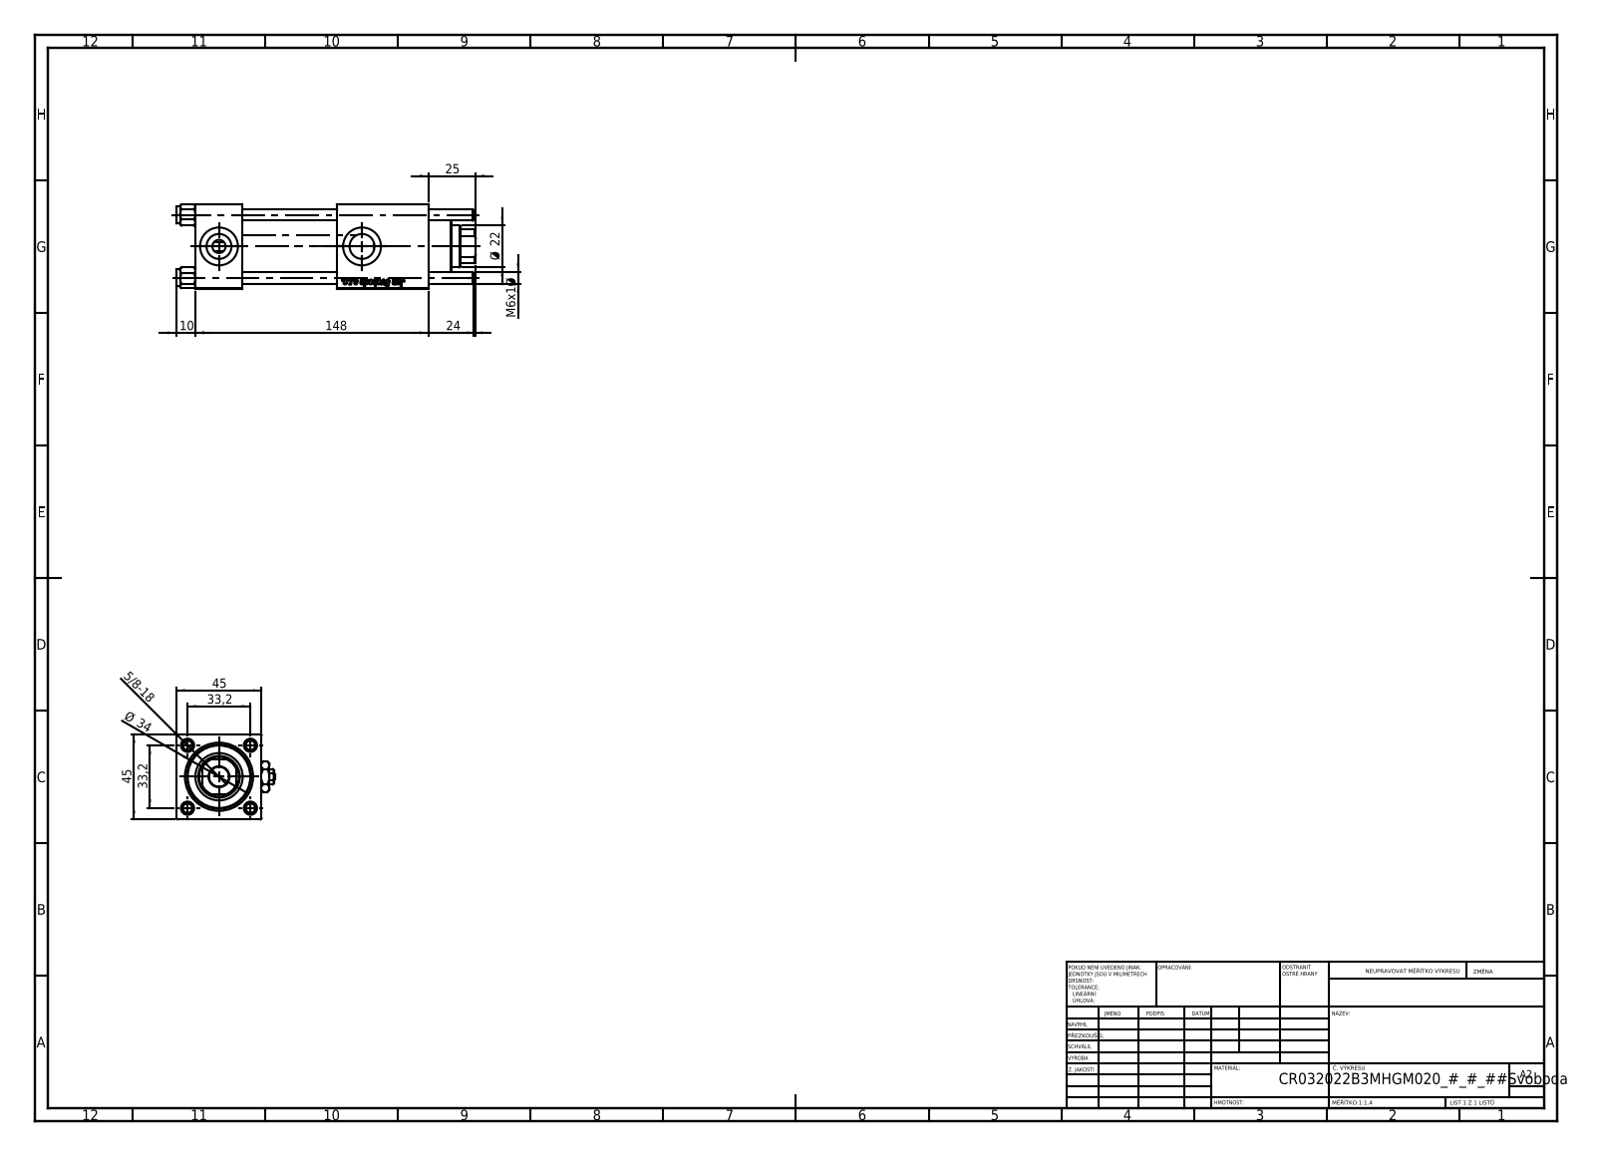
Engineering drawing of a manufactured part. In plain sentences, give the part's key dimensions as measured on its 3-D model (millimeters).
The part is named "Zatka_pro_OIL_PORT; V215_VC_A; V215CR_B_TYCINKA; NUT_M5_B (+2 more)". Its 3-D file was written by "SolidWorks 2019 (CONFIG_CONTROL_DESIGN)". It is 13 solids with 1256 faces: 478 planar, 88 cylindrical and 690 other. Overall it measures 158 by 52 by 45 millimeters. Its volume is 212 781 cubic millimeters and its surface area 78 630 square millimeters. Round holes: 4 of diameter 6, 2 of diameter 7, 2 of diameter 13.16, 2 of diameter 20, 1 of diameter 10.5, 1 of diameter 22, 1 of diameter 24, 1 of diameter 25, 1 of diameter 32, 1 of diameter 33. Round bosses or shafts: 4 of diameter 9, 1 of diameter 38, 1 of diameter 34. Partial cylindrical surfaces (rounded edges, fillets, slot ends): 1 of radius 10.5. The main face-to-face distances are 45, 25, 50, 123, 75, 44.8, 98, 48, 94.3, 69.3. The hole center spacings are 23.48, 33.2, 46.95, 75.5.
